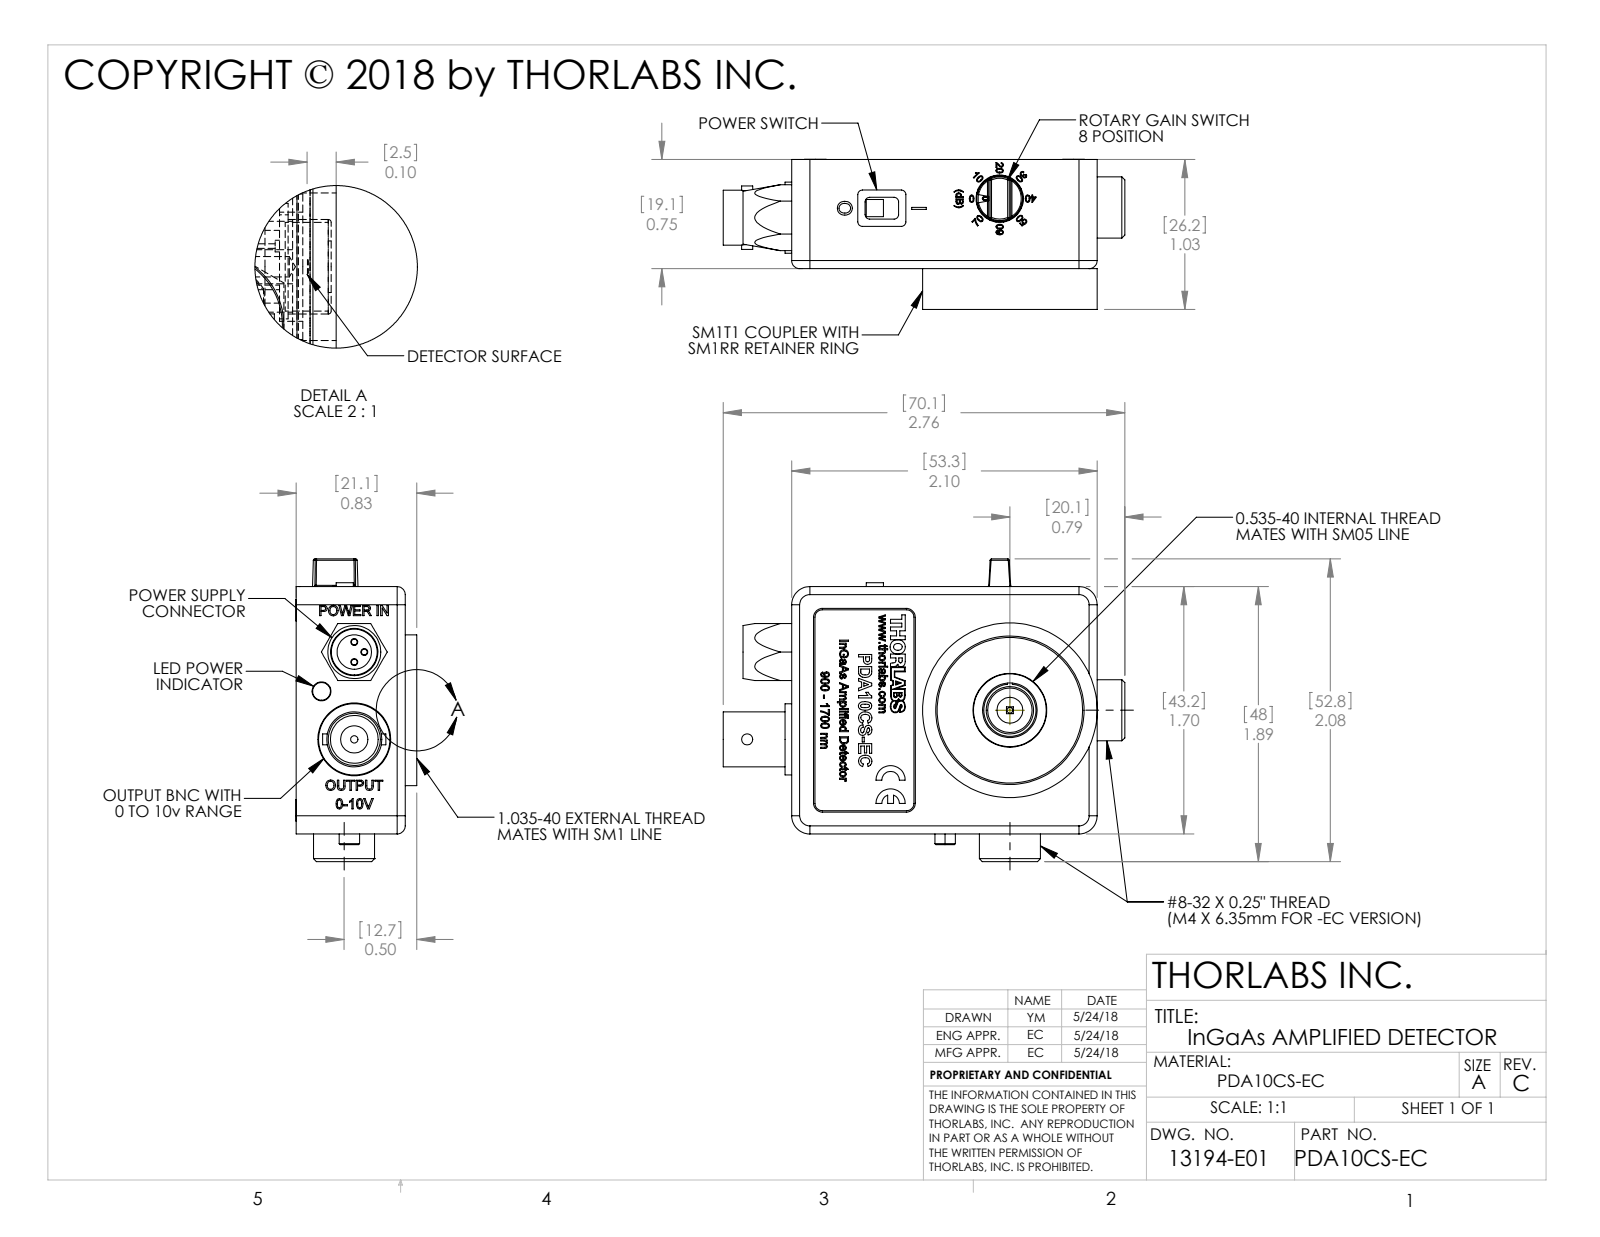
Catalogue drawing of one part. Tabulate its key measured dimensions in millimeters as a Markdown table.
| quantity | value |
| --- | --- |
| part name | 13194-E0W |
| STEP written by | SolidWorks 2011 (CONFIG_CONTROL_DESIGN) |
| units | millimeters |
| bodies | 0 solids, 546 faces (356 planar, 91 cylindrical, 99 other) |
| overall size | 70.1 × 52.3 × 27.5 |
| round holes (diameter × count) | 1 × 3, 3.3 × 2, 1.3 × 1, 3.3 × 1, 4.5 × 1, 8 × 1, 8.3 × 1, 8.3 × 1, 9.5 × 1, 9.8 × 1, 12.9 × 1, 25.4 × 1 |
| round bosses / shafts (diameter × count) | 3.7 × 4, 10.7 × 2, 30.5 × 1, 12.4 × 1, 9.6 × 1, 9.4 × 1, 8.3 × 1, 6 × 1 |
| partial cylindrical surfaces (radius × count) | 0.8 × 8, 2.4 × 8, 3.2 × 6, 1.4 × 4, 1.6 × 3, 1.3 × 2, 1.6 × 1, 1.9 × 1 |
| main face-to-face distances | 14.4, 1.6, 12.8, 12.8, 11.2, 1.6, 7.6, 20.3, 18.7, 6 |
| hole center spacings | 1.8, 2.5, 2.8, 3.5, 5.1, 5.4, 7.3, 8.6 |
